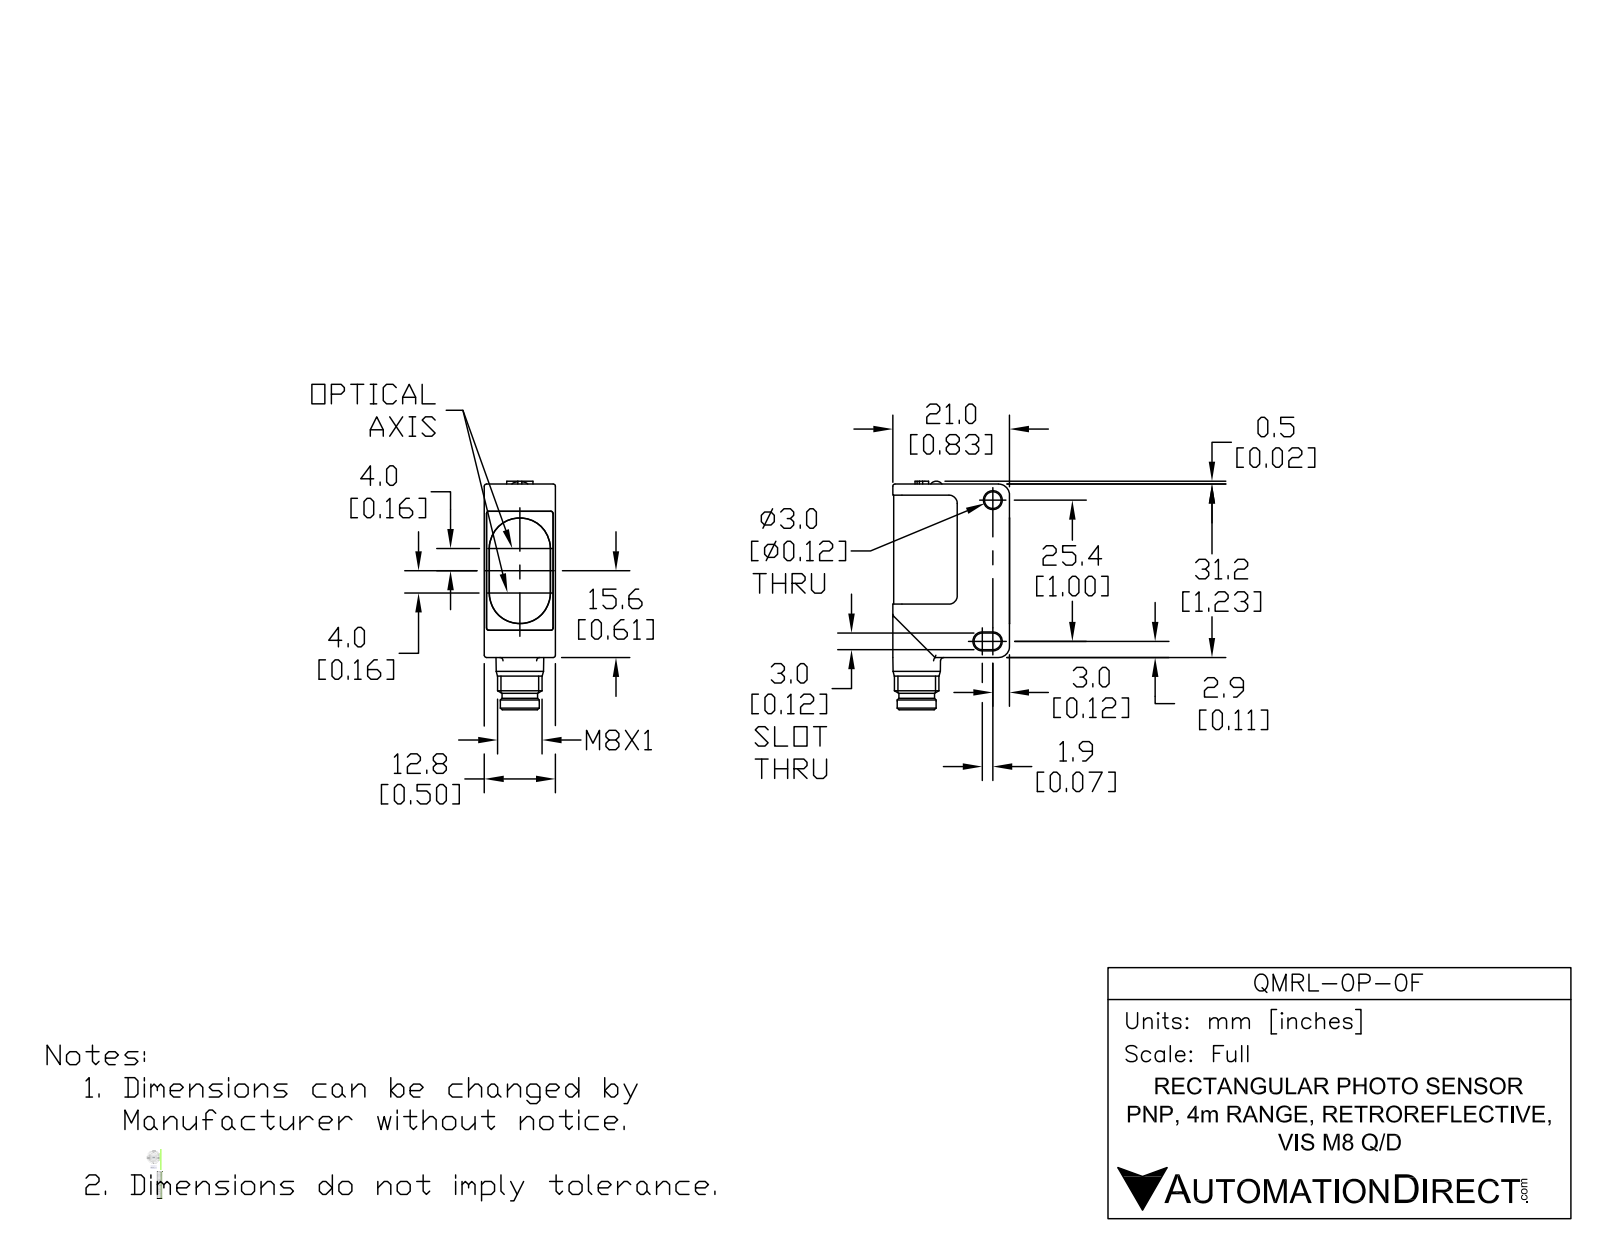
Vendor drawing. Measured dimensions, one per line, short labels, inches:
name: QMRL-0P-0F
written by: SolidWorks 2017 (AUTOMOTIVE_DESIGN)
unit: in
bodies: 7 solids, 272 faces (125 planar, 100 cylindrical, 47 other)
size: 1.619 × 0.827 × 0.504
volume: 0.474 in³; area: 7.749 in²
holes: 3× ⌀0.118, 1× ⌀0.228
bosses: 4× ⌀0.039, 2× ⌀0.138, 1× ⌀0.315, 1× ⌀0.276, 1× ⌀0.252
rounds: 10× R0.016, 9× R0.02, 6× R0.059, 4× R0.024, 4× R0.039, 2× R0.006, 2× R0.044, 2× R0.065
face distances: 0.498, 0.02, 0.504, 0.11, 0.016, 0.492, 0.488, 0.482, 0.059, 0.711
hole spacings: 0.04, 0.205, 0.245
